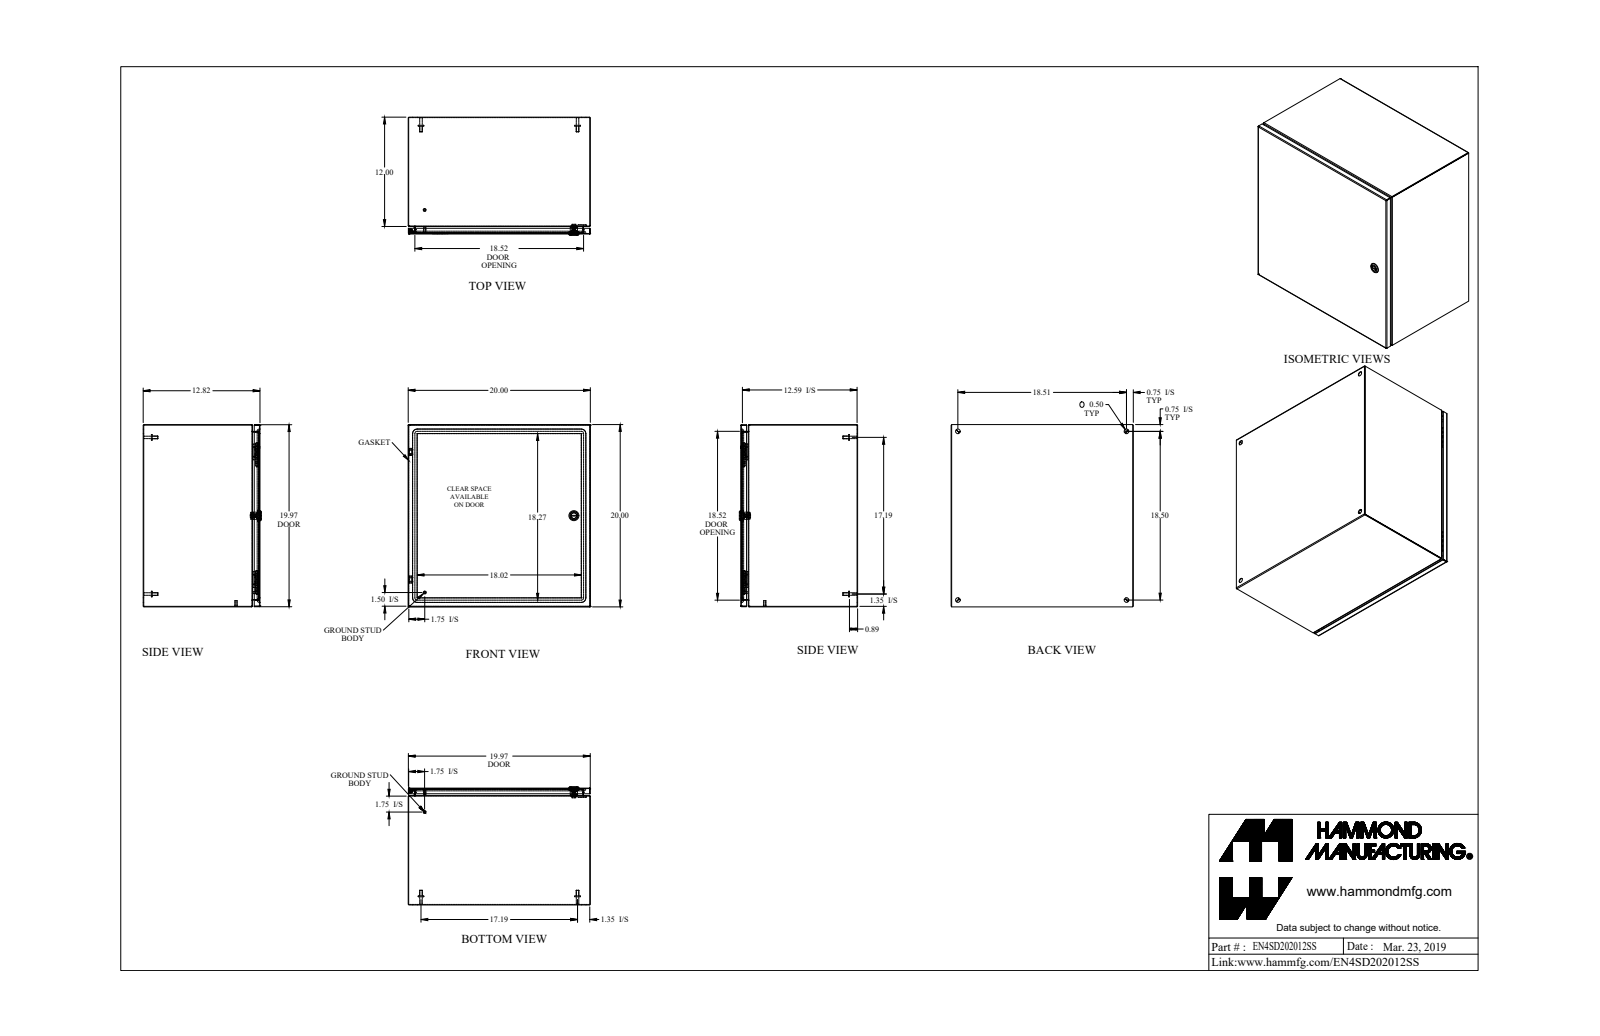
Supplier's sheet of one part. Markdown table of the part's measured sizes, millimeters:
| quantity | value |
| --- | --- |
| part name | EN4SD202012SS_Default |
| STEP written by | SolidWorks 2019 (CONFIG_CONTROL_DESIGN) |
| units | millimeters |
| bodies | 24 solids, 645 faces (303 planar, 208 cylindrical, 134 other) |
| overall size | 508 × 508 × 329.7 |
| volume | 1 916 000 mm³ |
| surface area | 2 588 000 mm² |
| round holes (diameter × count) | 12.7 × 5, 4.4 × 1, 5 × 1, 6.1 × 1, 6.1 × 1, 9.8 × 1, 16 × 1, 19.5 × 1 |
| round bosses / shafts (diameter × count) | 8 × 6, 15.9 × 5, 7 × 4, 6.4 × 2, 27.9 × 1, 19.9 × 1, 13.3 × 1, 11.6 × 1 |
| partial cylindrical surfaces (radius × count) | 0.7 × 19, 2.2 × 19, 4.8 × 12, 0.2 × 4, 1.6 × 4, 6.4 × 4, 12.7 × 4, 3.2 × 2 |
| main face-to-face distances | 1.4, 506.6, 324.2, 505.1, 508, 322.8, 325.7, 20.9, 303.4, 19.4 |
| hole center spacings | 236.5, 469.9, 470.3, 501.4, 664.8 |
